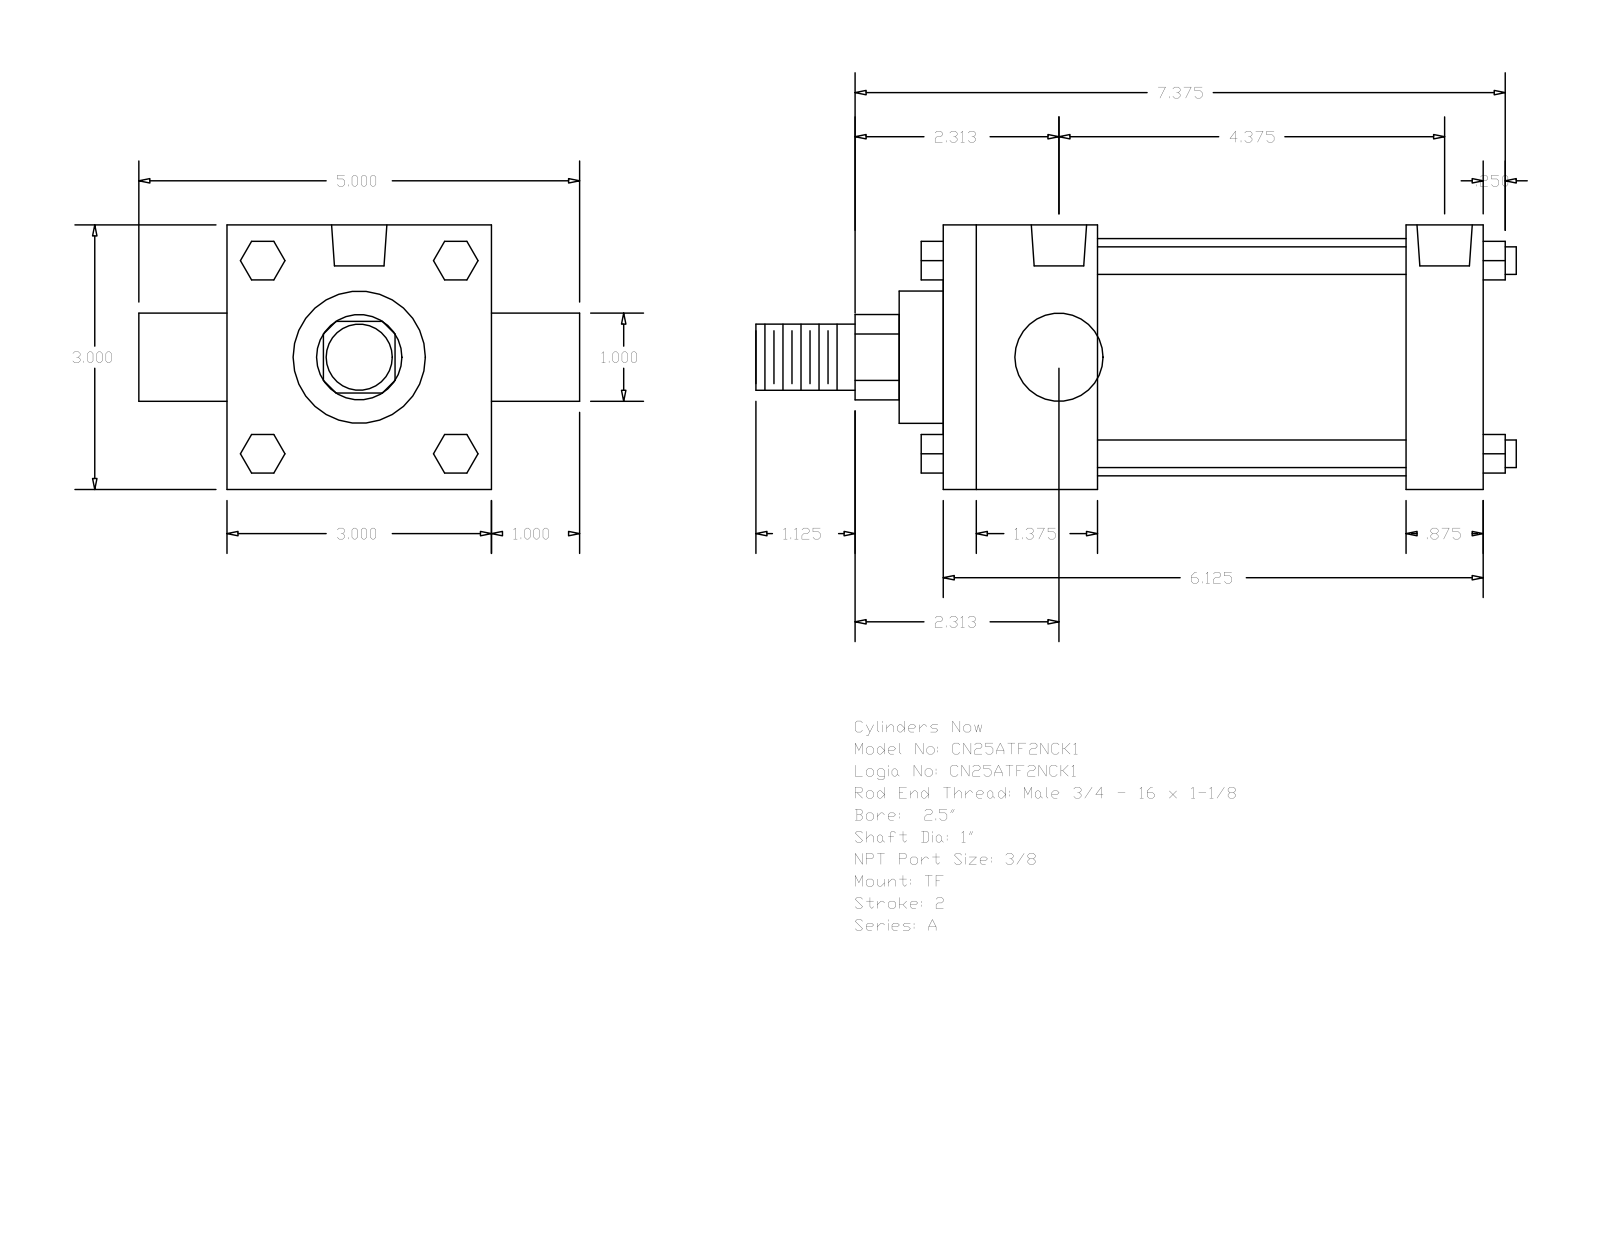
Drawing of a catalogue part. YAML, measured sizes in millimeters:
part_name: "A_TF__0250_1"
step_written_by: "GSSL Pune (CONFIG_CONTROL_DESIGN)"
units: millimeters
bodies: {solids: 0, faces: 120, planar: 92, cylindrical: 28, other: 0}
overall_size: [219.07, 127, 76.2]
round_holes:
  - {diameter: 5.56, count: 3}
  - {diameter: 15.93, count: 2}
round_bosses_or_shafts:
  - {diameter: 7.94, count: 4}
  - {diameter: 25.4, count: 2}
  - {diameter: 68.33, count: 1}
  - {diameter: 38.1, count: 1}
  - {diameter: 19.05, count: 1}
partial_cylinders:
  - {radius: 12.29, count: 1}
face_to_face_distances: [76.2, 155.57, 44.45, 133.35, 88.9, 111.12, 22.22, 25.4, 101.6, 168.27]
hole_center_spacings: [2.38, 113.5, 111.12, 115.88]
